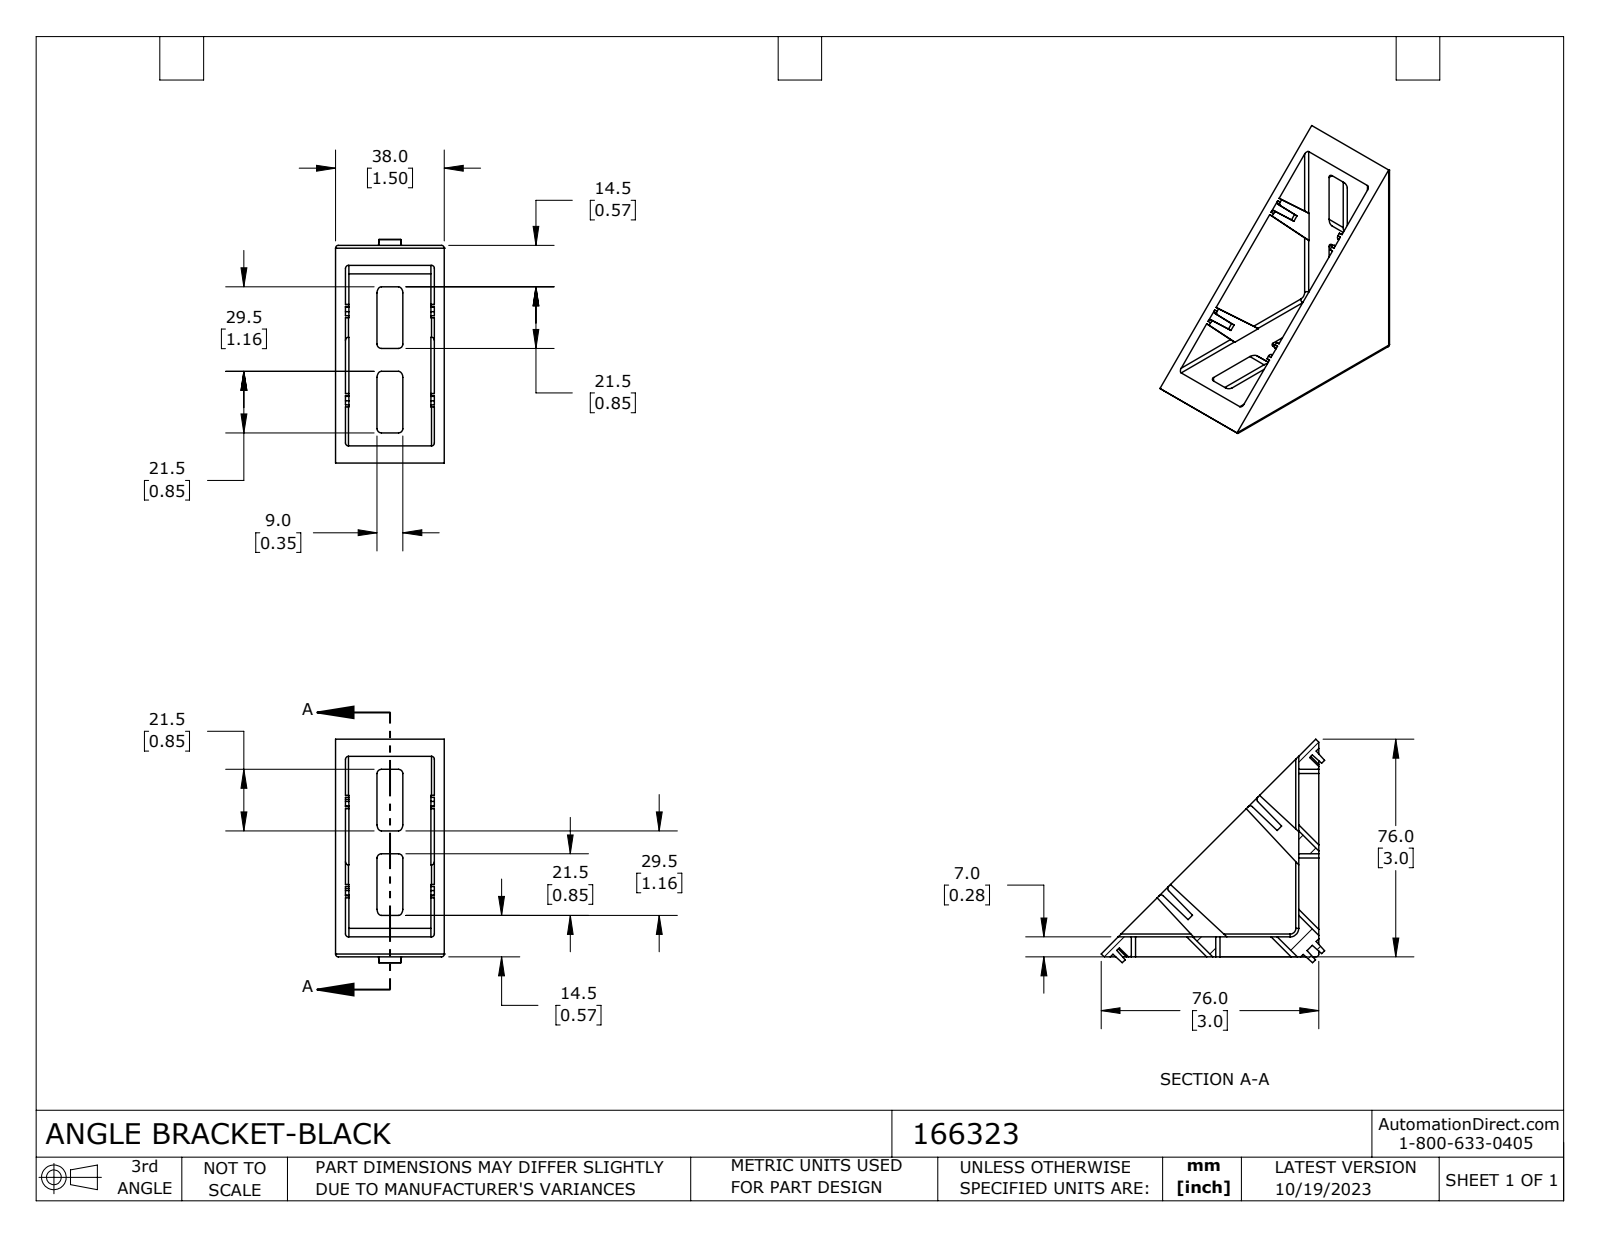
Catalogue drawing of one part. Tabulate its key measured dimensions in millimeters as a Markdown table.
| quantity | value |
| --- | --- |
| part name | 166323 |
| STEP written by | SolidWorks 2023 (CONFIG_CONTROL_DESIGN) |
| units | millimeters |
| bodies | 1 solid, 345 faces (146 planar, 141 cylindrical, 58 other) |
| overall size | 78.04 × 78.04 × 38 |
| volume | 40 725 mm³ |
| surface area | 22 939 mm² |
| partial cylindrical surfaces (radius × count) | 0.5 × 72, 1.5 × 16, 1 × 13, 3 × 1 |
| main face-to-face distances | 3.5, 34.5, 38, 7, 3, 31, 23.5, 4, 14.5, 11 |
